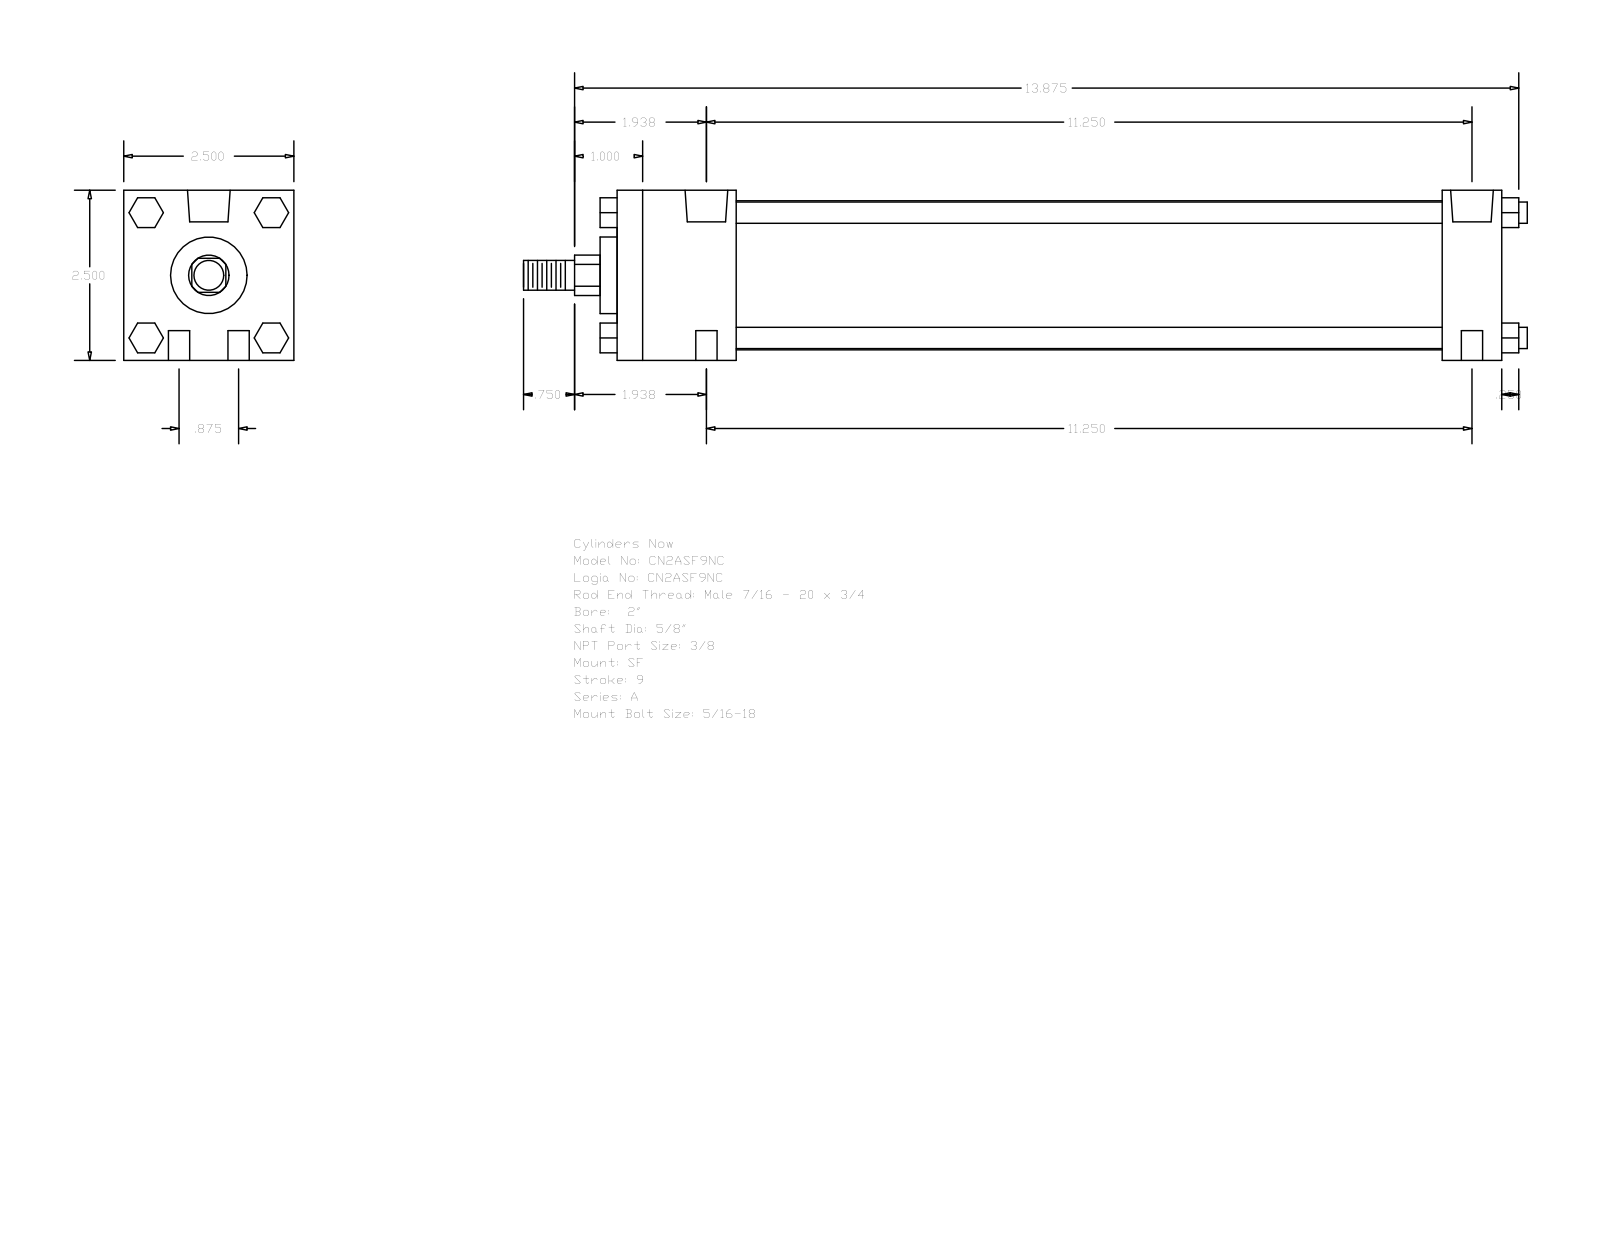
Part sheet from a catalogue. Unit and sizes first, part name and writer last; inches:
Units: inches
Overall size (bounding box): 14.75 × 2.5 × 2.5
Round holes (diameter × count): ⌀0.313 ×4, ⌀0.219 ×2, ⌀0.627 ×2
Round bosses / shafts (diameter × count): ⌀0.313 ×4, ⌀2.19 ×1, ⌀1.125 ×1, ⌀0.625 ×1, ⌀0.437 ×1
Partial cylindrical surfaces — rounded edges, fillets, slot ends (radius × count): R0.297 ×1
Main face-to-face distances: 2.5, 13, 12.125, 0.875, 1.75, 10.375, 11.25, 2, 0.25, 12.375
Hole centre spacings: 0.437, 11.259, 11.25, 0.875, 11.284, 10.937
Bodies: 0 solids, 124 faces (94 planar, 30 cylindrical, 0 other)
Part name (STEP PRODUCT): A_SF__0200_0.625
STEP written by: GSSL Pune (CONFIG_CONTROL_DESIGN)
